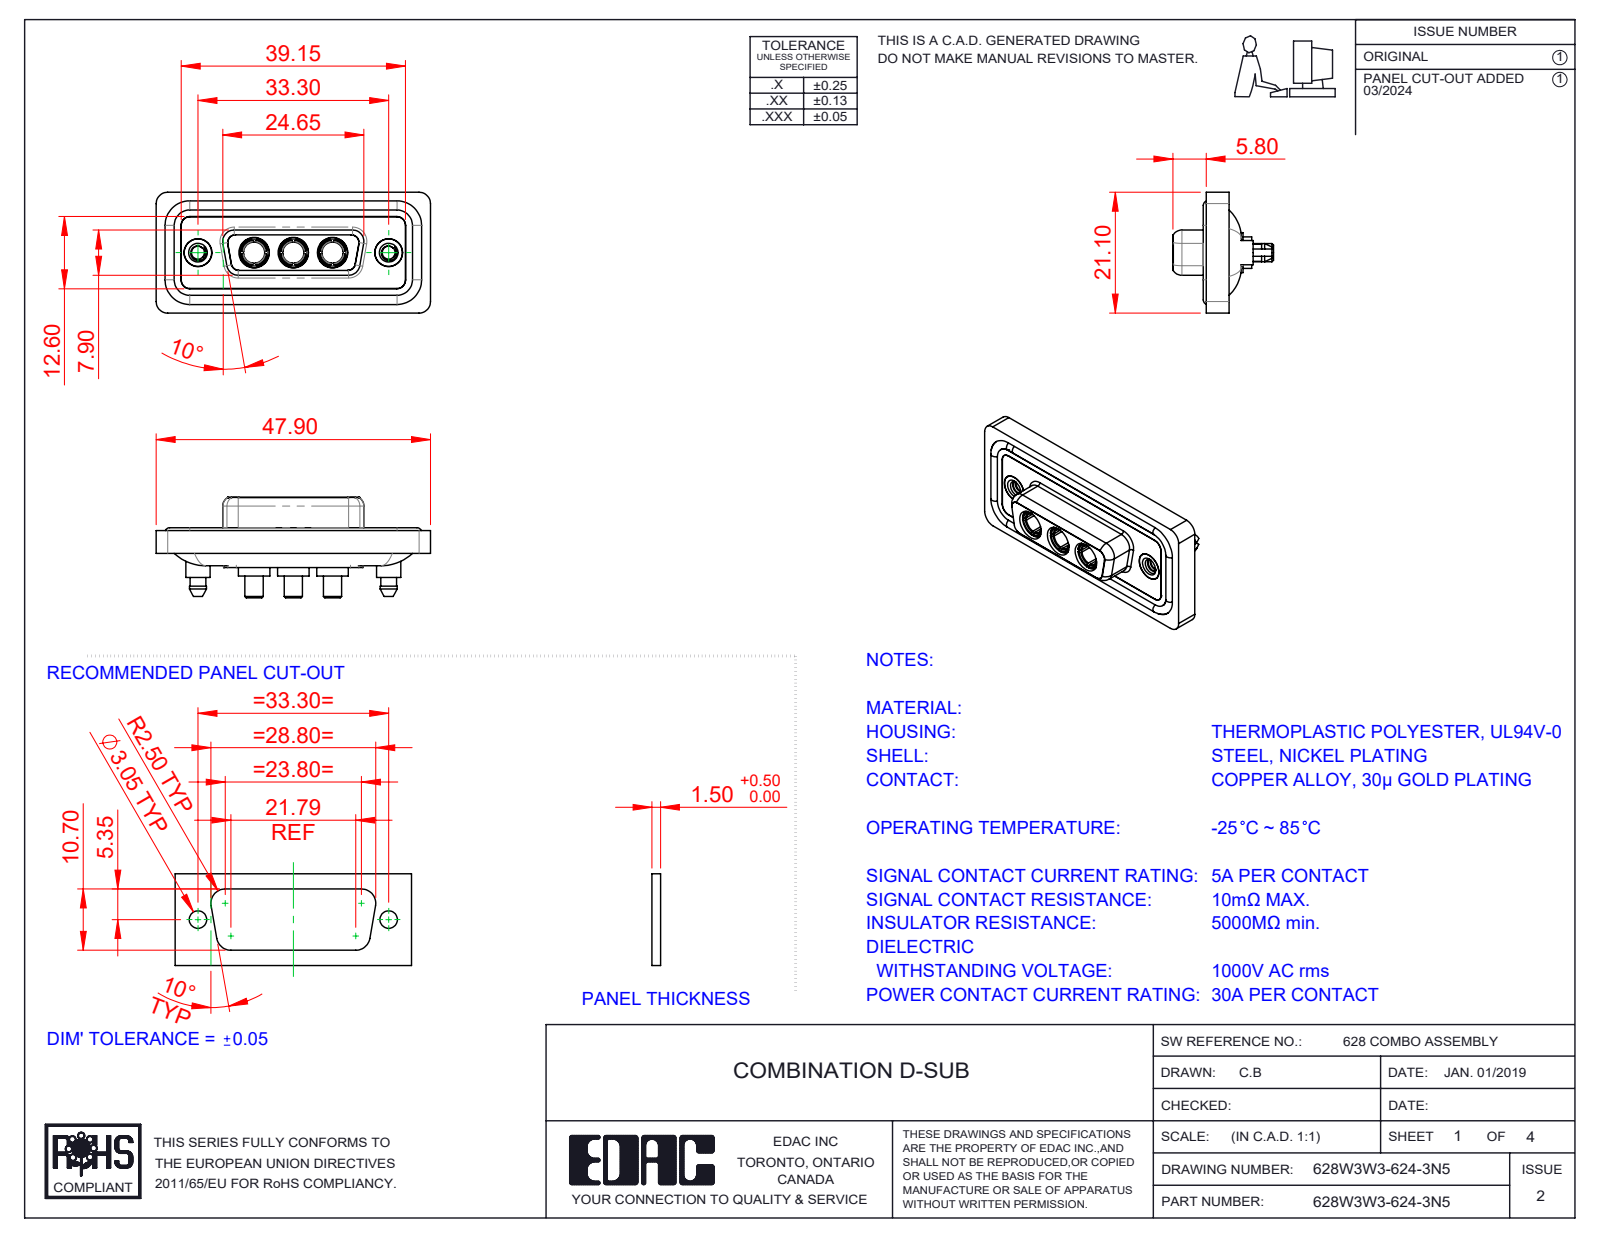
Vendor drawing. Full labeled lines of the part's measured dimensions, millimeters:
Part name (STEP PRODUCT): 628Combo Waterproof Housing_15 Contacts; 628Combo Shell Rear_15 Contacts; 628Combo Shell Front_15 Contacts; Power Socket_30A S (+3 more)
STEP written by: SolidWorks 2023 (CONFIG_CONTROL_DESIGN)
Units: millimetres
Bodies: 13 solids, 658 faces (208 planar, 289 cylindrical, 161 other)
Overall size (bounding box): 47.9 × 21.1 × 17.55
Volume: 6 181 mm³ · Surface area: 10 085 mm²
Round holes (diameter × count): ⌀4.85 ×5, ⌀3.7 ×3, ⌀5.3 ×3, ⌀2.26 ×2, ⌀4 ×2, ⌀4.05 ×2, ⌀5 ×2
Round bosses / shafts (diameter × count): ⌀1.6 ×4, ⌀5.5 ×3, ⌀5.2 ×3, ⌀4.96 ×3, ⌀4.75 ×3, ⌀3.75 ×3, ⌀3.2 ×3, ⌀5.4 ×2
Partial cylindrical surfaces — rounded edges, fillets, slot ends (radius × count): R1.5 ×24, R2 ×20, R1.35 ×12, R1.6 ×10, R0.25 ×4, R0.5 ×4, R0.6 ×4, R0.65 ×4
Main face-to-face distances: 0.4, 1.8, 1.6, 0.5, 7.45, 1.1, 2.9, 5.65, 7.05, 6.6
Hole centre spacings: 6.85, 9.8, 16.65, 23.5, 13.7, 33.3
